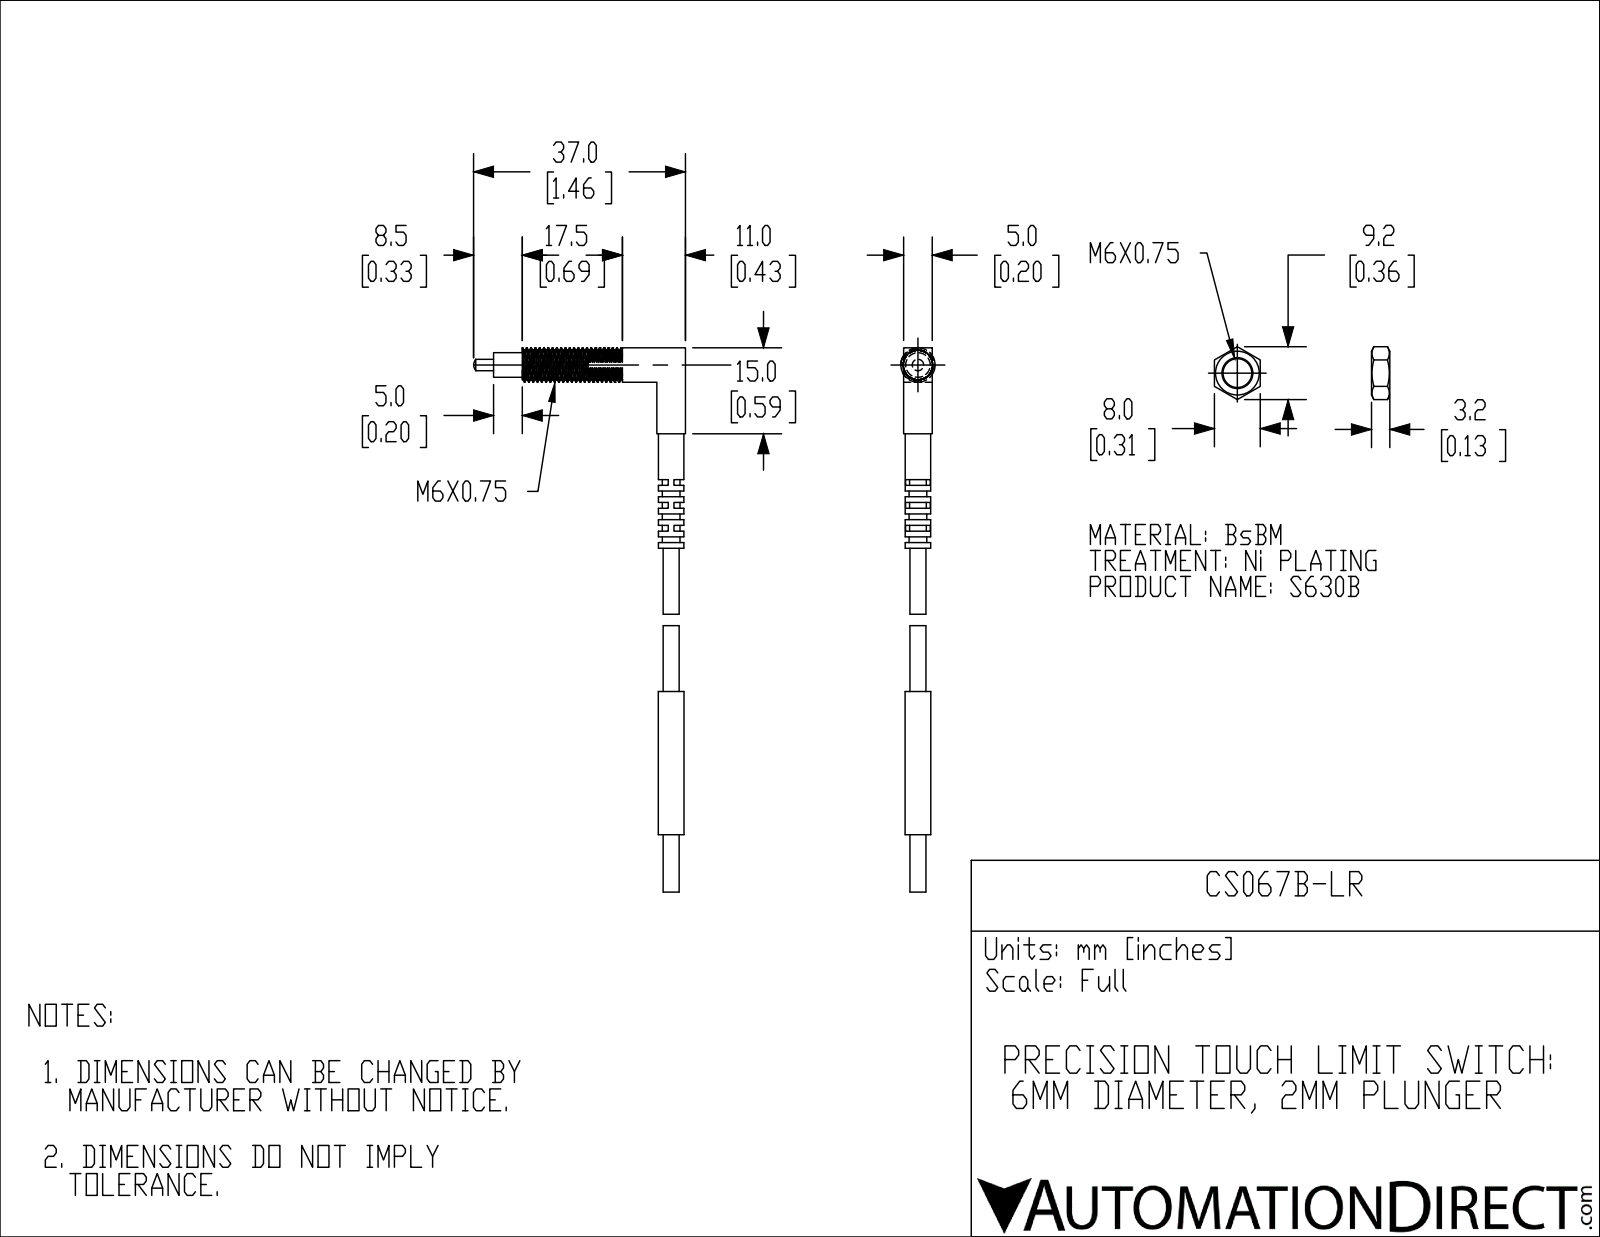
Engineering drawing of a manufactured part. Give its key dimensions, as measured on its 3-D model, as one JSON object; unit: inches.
{"part_name": "CS067B-LR", "step_written_by": "SolidWorks 2018 (AUTOMOTIVE_DESIGN)", "units": "inches", "bodies": {"solids": 2, "faces": 72, "planar": 51, "cylindrical": 20, "other": 1}, "overall_size": [3.74, 1.457, 0.236], "volume_in3": 0.121, "surface_area_in2": 2.988, "round_bosses_or_shafts": [[0.236, 1], [0.177, 1], [0.175, 1], [0.169, 1], [0.122, 1], [0.11, 1], [0.079, 1]], "face_to_face_distances": [0.197, 0.039, 0.236, 0.079, 0.118, 0.157, 0.354, 0.315, 0.276, 0.394]}
